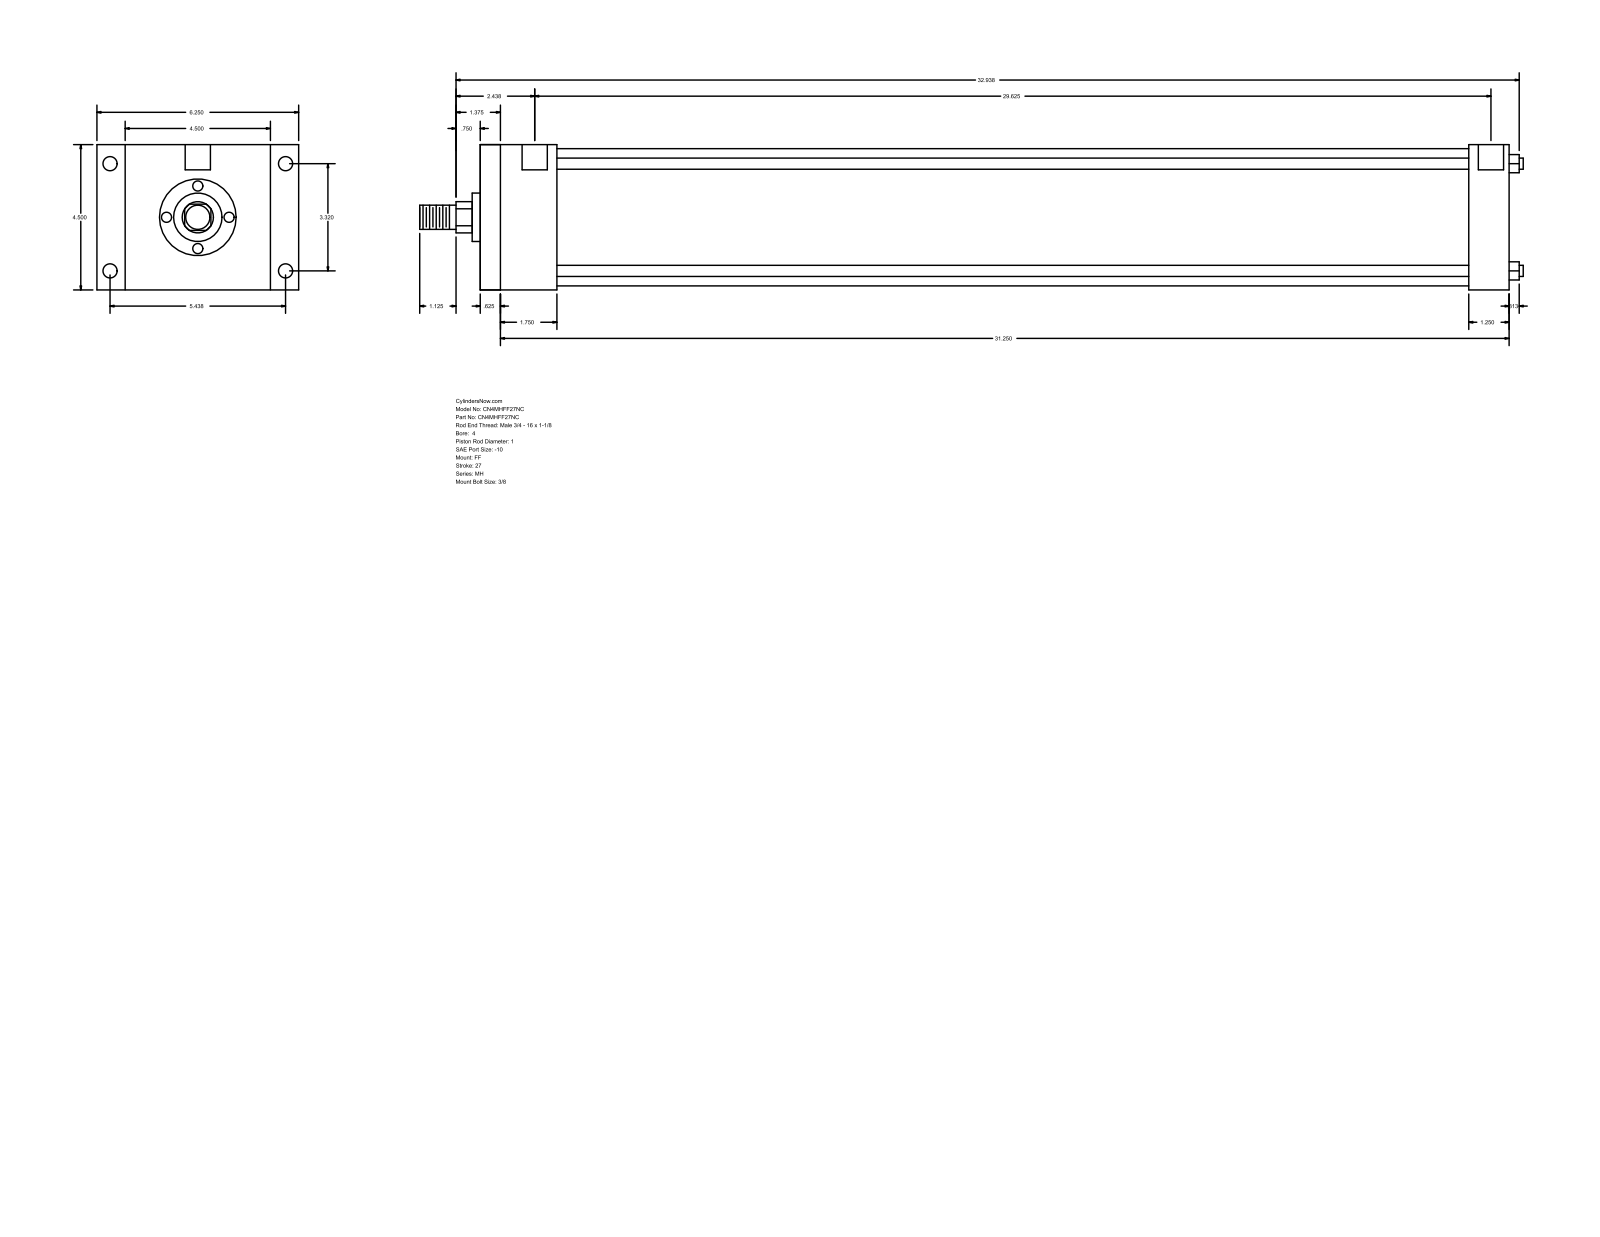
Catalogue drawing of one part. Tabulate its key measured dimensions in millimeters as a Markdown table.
| quantity | value |
| --- | --- |
| part name | MH_FF__0400_1 |
| STEP written by | GSSL Pune (CONFIG_CONTROL_DESIGN) |
| units | millimeters |
| bodies | 0 solids, 92 faces (64 planar, 28 cylindrical, 0 other) |
| overall size | 868.36 × 158.75 × 114.3 |
| round holes (diameter × count) | 8.73 × 4, 11.13 × 4, 19.84 × 2 |
| round bosses / shafts (diameter × count) | 8.76 × 4, 107.95 × 1, 38.1 × 1, 25.4 × 1, 19.05 × 1 |
| partial cylindrical surfaces (radius × count) | 12.29 × 1 |
| main face-to-face distances | 114.3, 809.62, 15.87, 793.75, 60.33, 44.46, 749.29, 777.87, 762, 717.54 |
| hole center spacings | 84.32, 138.12, 161.82, 755.65, 1.58, 1.59, 752.48, 754.06 |
